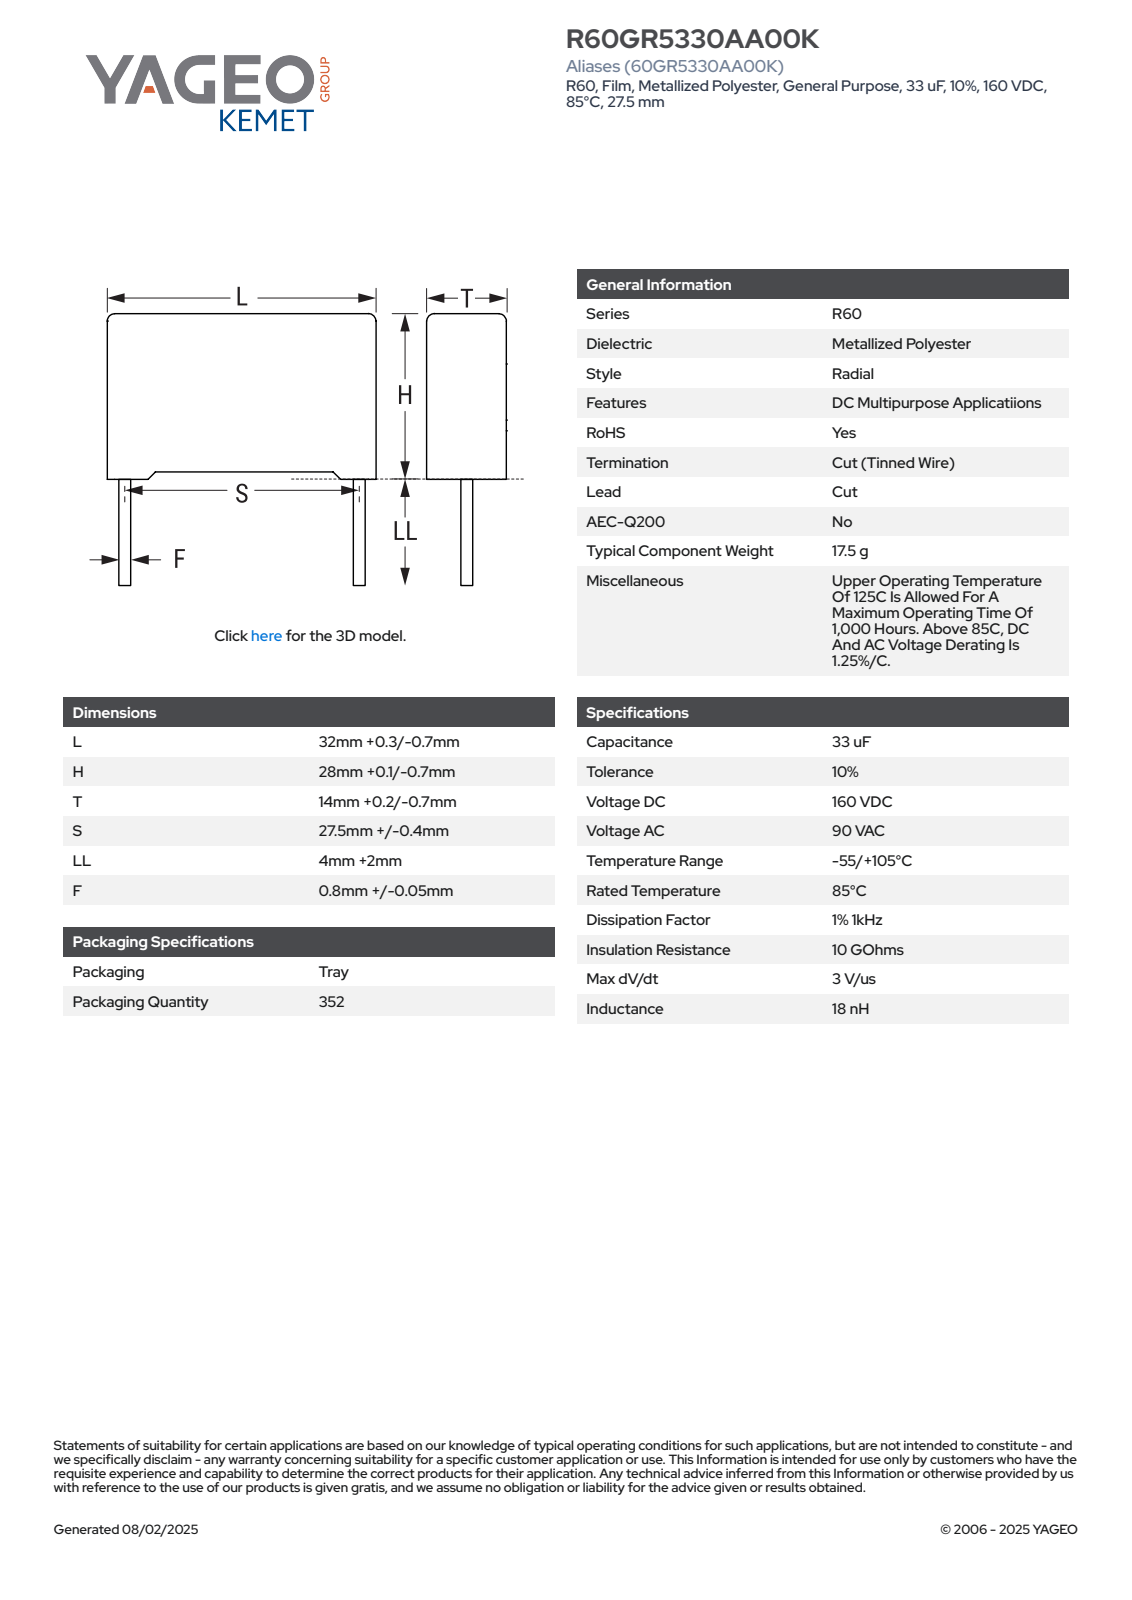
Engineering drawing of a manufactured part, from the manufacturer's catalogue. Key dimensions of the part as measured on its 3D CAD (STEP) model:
Part name (STEP PRODUCT): CFR_RB2_32X28X14_L32.3H28.1T14.2S27.5LL6F0.85
STEP written by: SolidWorks 2021 (AUTOMOTIVE_DESIGN)
Units: millimetres
Bodies: 4 solids, 85 faces (77 planar, 8 cylindrical, 0 other)
Overall size (bounding box): 34.1 × 32.3 × 14.21
Volume: 12 509 mm³ · Surface area: 3 611 mm²
Round bosses / shafts (diameter × count): ⌀0.85 ×2
Partial cylindrical surfaces — rounded edges, fillets, slot ends (radius × count): R0.5 ×4
Main face-to-face distances: 14.2, 32.3, 27.13, 27.35, 0.75, 0.97, 28.1, 1.08, 31.22, 13.12
